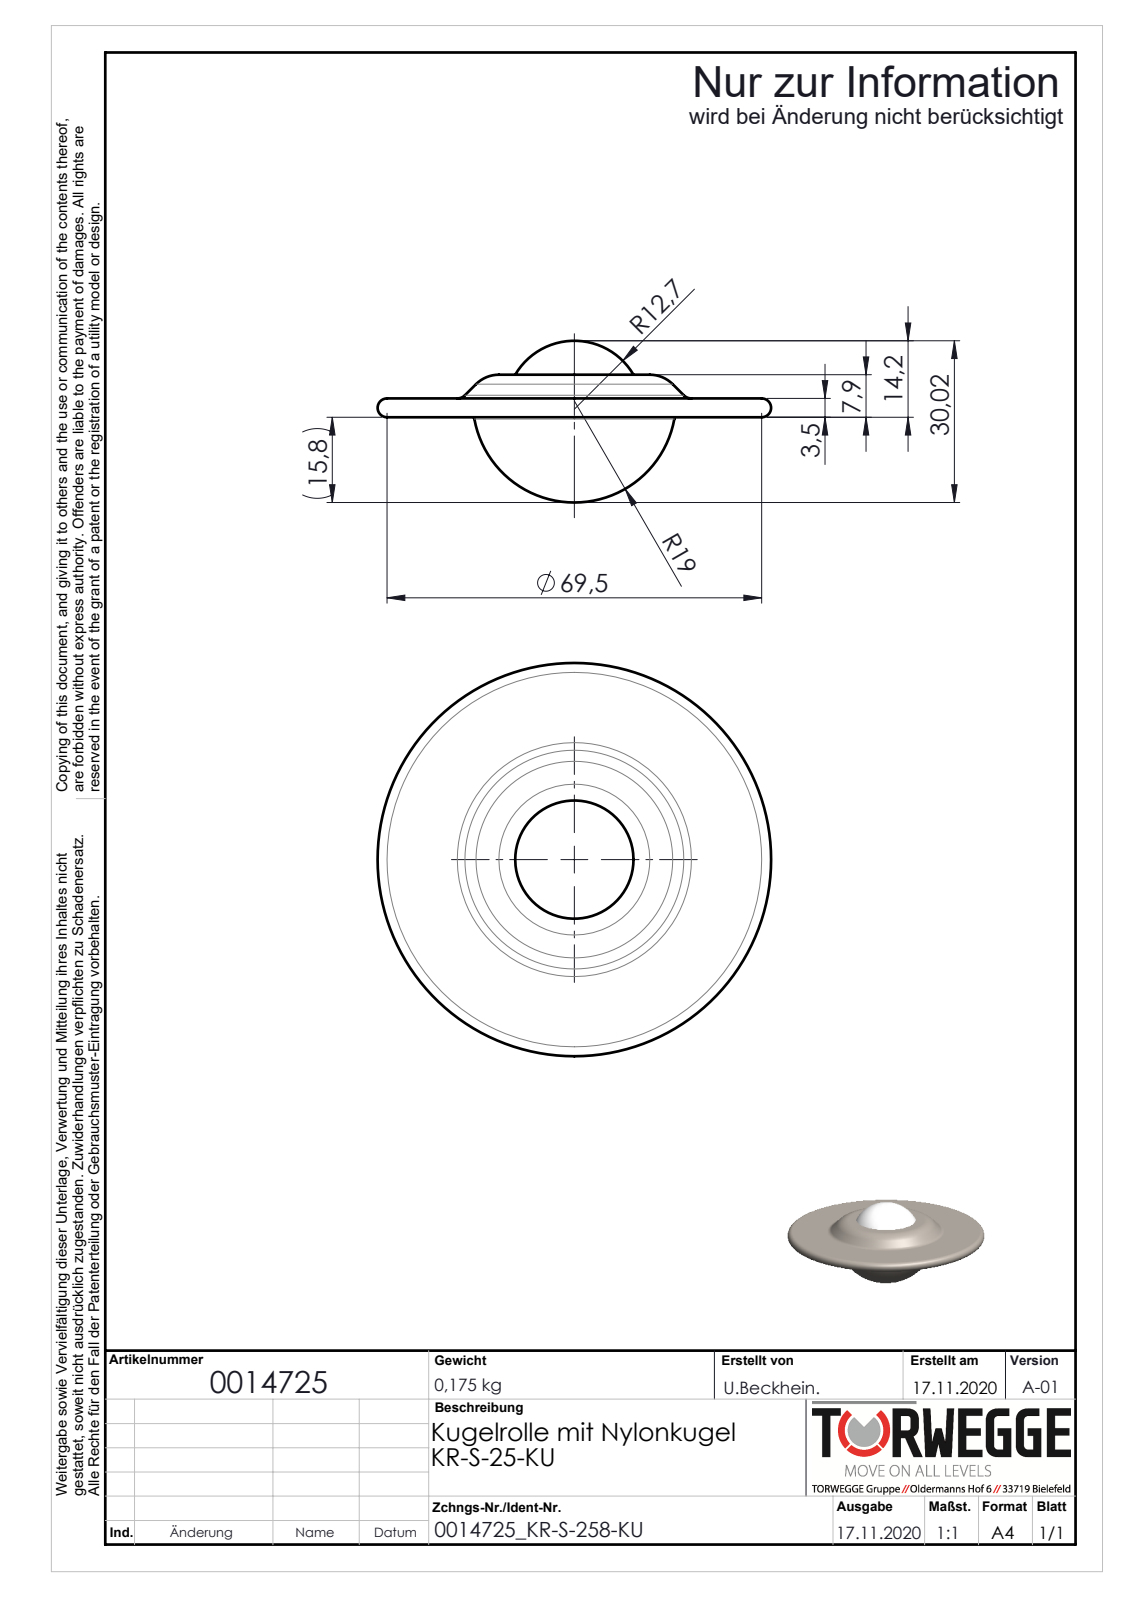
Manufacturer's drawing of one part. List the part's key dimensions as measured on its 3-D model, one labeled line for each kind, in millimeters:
Part name (STEP PRODUCT): 0014725
STEP written by: SolidWorks 2018 (AUTOMOTIVE_DESIGN)
Units: millimetres
Bodies: 1 solid, 21 faces (4 planar, 2 cylindrical, 15 other)
Overall size (bounding box): 73 × 73 × 29.85
Volume: 29 188 mm³ · Surface area: 10 134 mm²
Round holes (diameter × count): ⌀64.8 ×1
Main face-to-face distances: 2.6, 0.9, 3.5, 7.9, 7, 4.4
